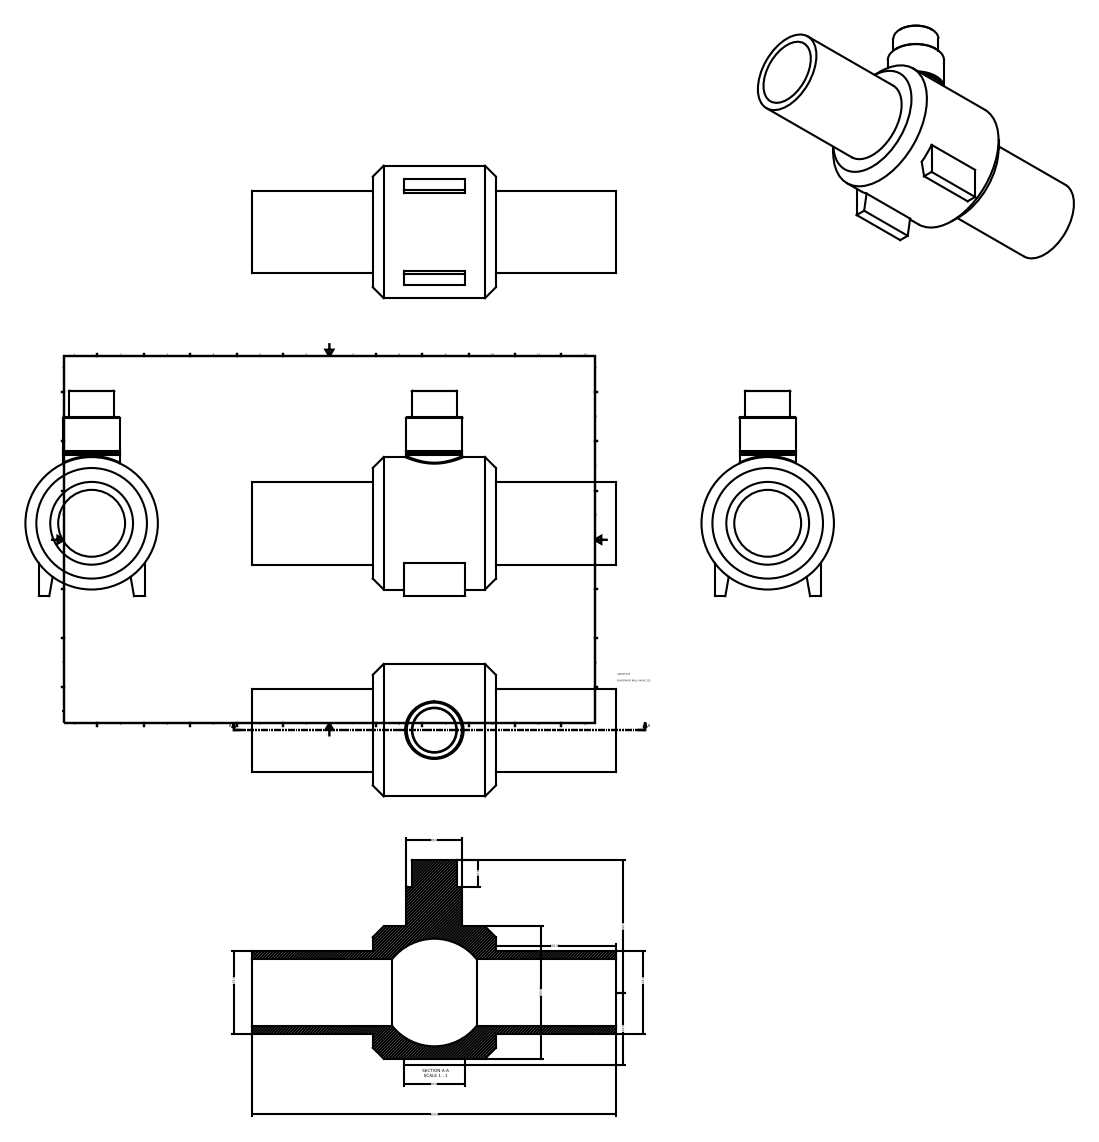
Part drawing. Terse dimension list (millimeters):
name: 436207125
written by: Autodesk Inventor 2015 (AUTOMOTIVE_DESIGN)
unit: mm
bodies: 1 solid, 33 faces (16 planar, 9 cylindrical, 8 other)
size: 550 × 310 × 200
volume: 5 298 000 mm³; area: 533 892 mm²
holes: 1× ⌀101
bosses: 1× ⌀200, 1× ⌀125, 1× ⌀85, 1× ⌀68
face distances: 186, 182, 368, 160, 550, 310, 228.5, 321.5, 46.5, 139.5
